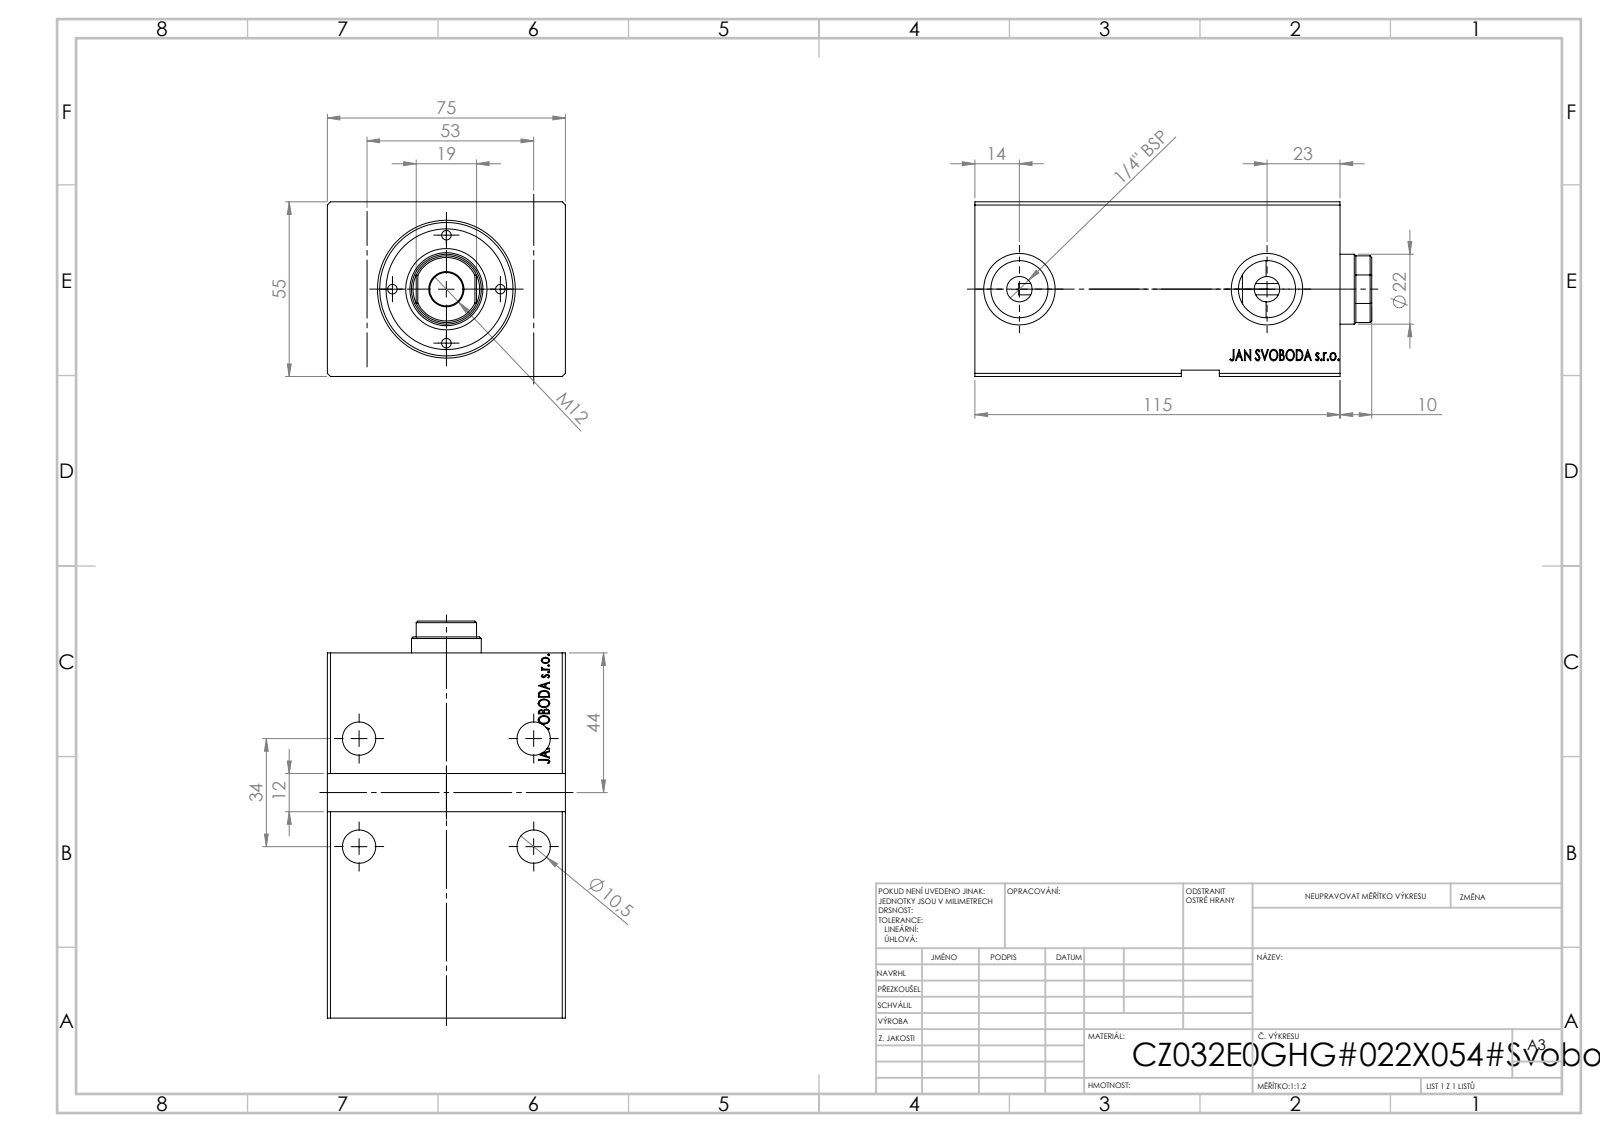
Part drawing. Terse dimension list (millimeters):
written by: SolidWorks 2019 (CONFIG_CONTROL_DESIGN)
unit: mm
bodies: 1 solid, 751 faces (367 planar, 32 cylindrical, 352 other)
size: 115 × 75 × 55
volume: 359 218 mm³; area: 56 520 mm²
holes: 4× ⌀8, 4× ⌀10.5, 2× ⌀18, 2× ⌀22.5, 1× ⌀32, 1× ⌀36, 1× ⌀42
face distances: 55, 75, 115, 13.6, 114.8, 2, 53, 101.2, 13.8, 10
hole spacings: 34, 55, 64.66, 18.5, 33.02, 34.73, 37.98, 46.8
